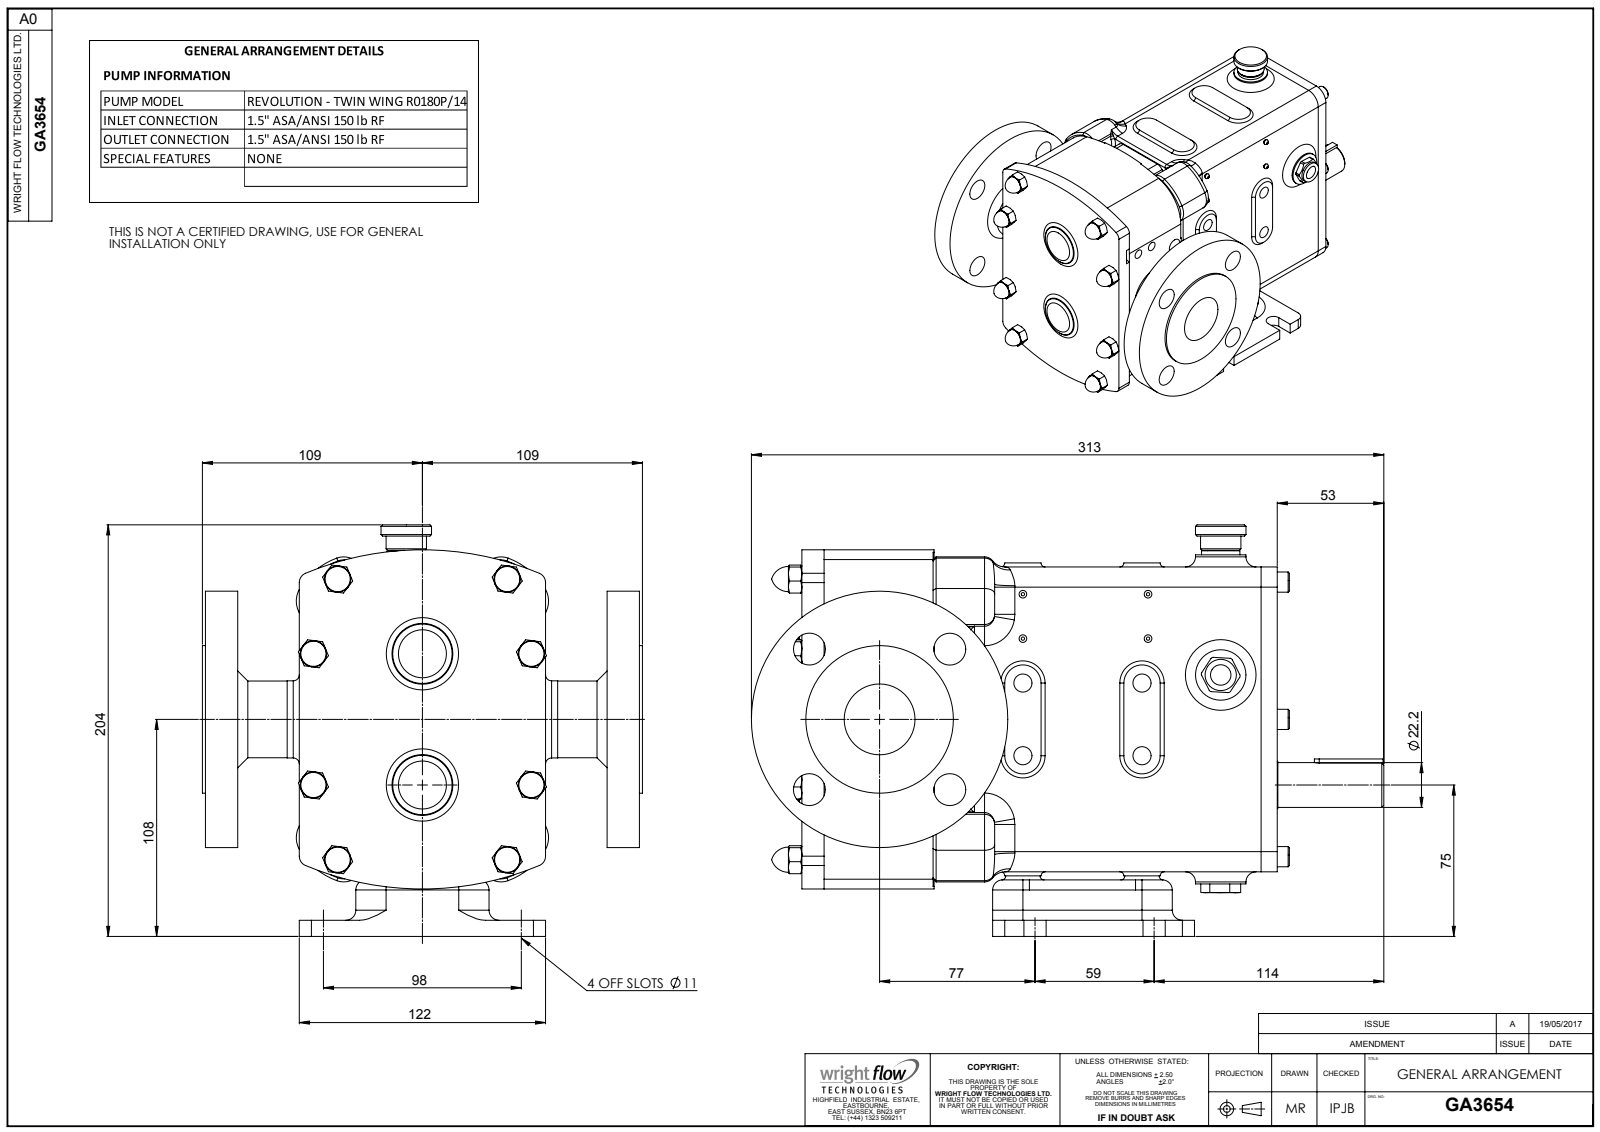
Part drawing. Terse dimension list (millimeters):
name: Copy of R0180 CPP H BSD^GA3654; Copy of Z94-5301-22 - 1.5 INCH ASA 150^GA3654; GA3654
written by: SolidWorks 2023 (AUTOMOTIVE_DESIGN)
unit: mm
bodies: 3 solids, 1216 faces (372 planar, 333 cylindrical, 511 other)
size: 313.3 × 218 × 203.86
volume: 4 046 000 mm³; area: 304 250 mm²
holes: 6× ⌀15.8, 4× ⌀7, 4× ⌀9, 2× ⌀11, 1× ⌀22.53, 1× ⌀35.1
bosses: 6× ⌀10, 4× ⌀25, 4× ⌀13, 1× ⌀127, 1× ⌀73.1, 1× ⌀38.2, 1× ⌀38, 1× ⌀25.02
rounds: 28× R2, 26× R10, 19× R5, 14× R6, 8× R8, 6× R1.27, 4× R1.25, 4× R5.5
face distances: 134.5, 16, 48.5, 64.5, 183, 150.5, 199, 86, 152.5, 46.5
hole spacings: 49.2, 69.58, 86.77, 14, 14.97, 19.1, 19.15, 26.61
